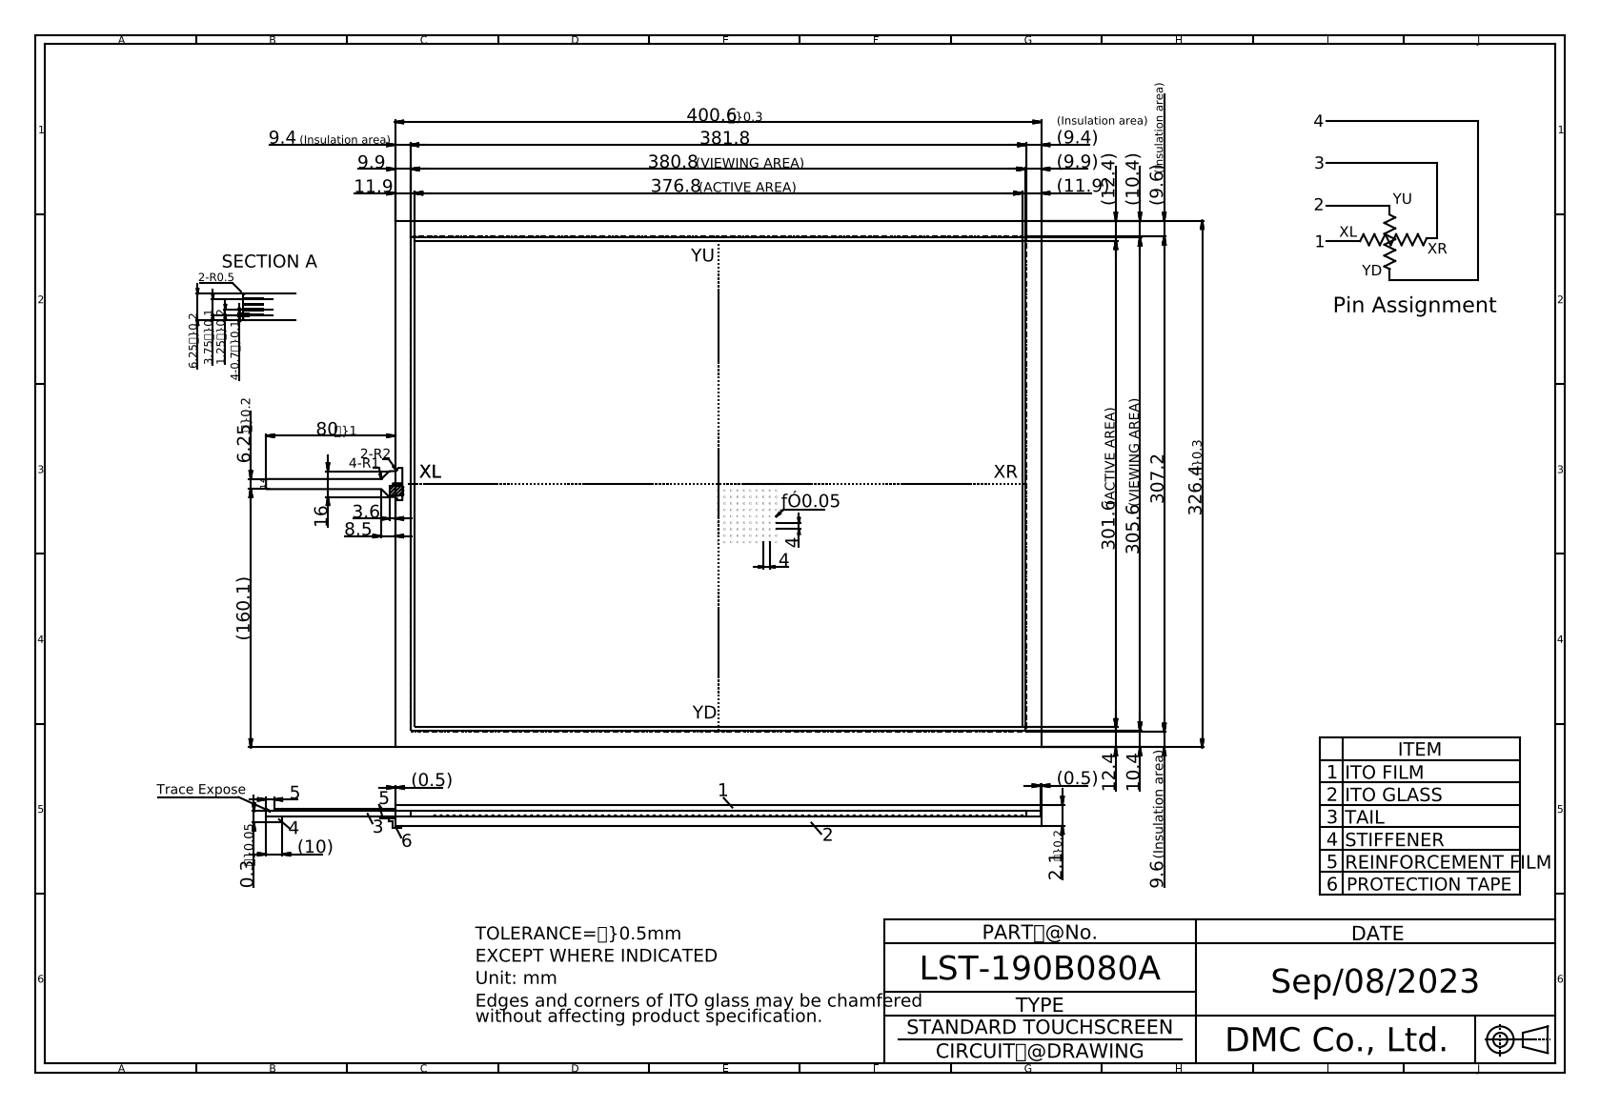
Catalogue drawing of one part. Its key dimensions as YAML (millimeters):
part_name: "LST-190B080A"
step_written_by: "Autodesk Inventor 2020 (CONFIG_CONTROL_DESIGN)"
units: millimeters
bodies: {solids: 1, faces: 51, planar: 45, cylindrical: 6, other: 0}
overall_size: [480.6, 326.4, 2.1]
volume: 274386
surface_area: 265981
partial_cylinders:
  - {radius: 1, count: 4}
  - {radius: 0.5, count: 2}
face_to_face_distances: [2.1, 2, 326.4, 400.6, 1.91, 1.81, 10.4, 316, 12.4, 314]
